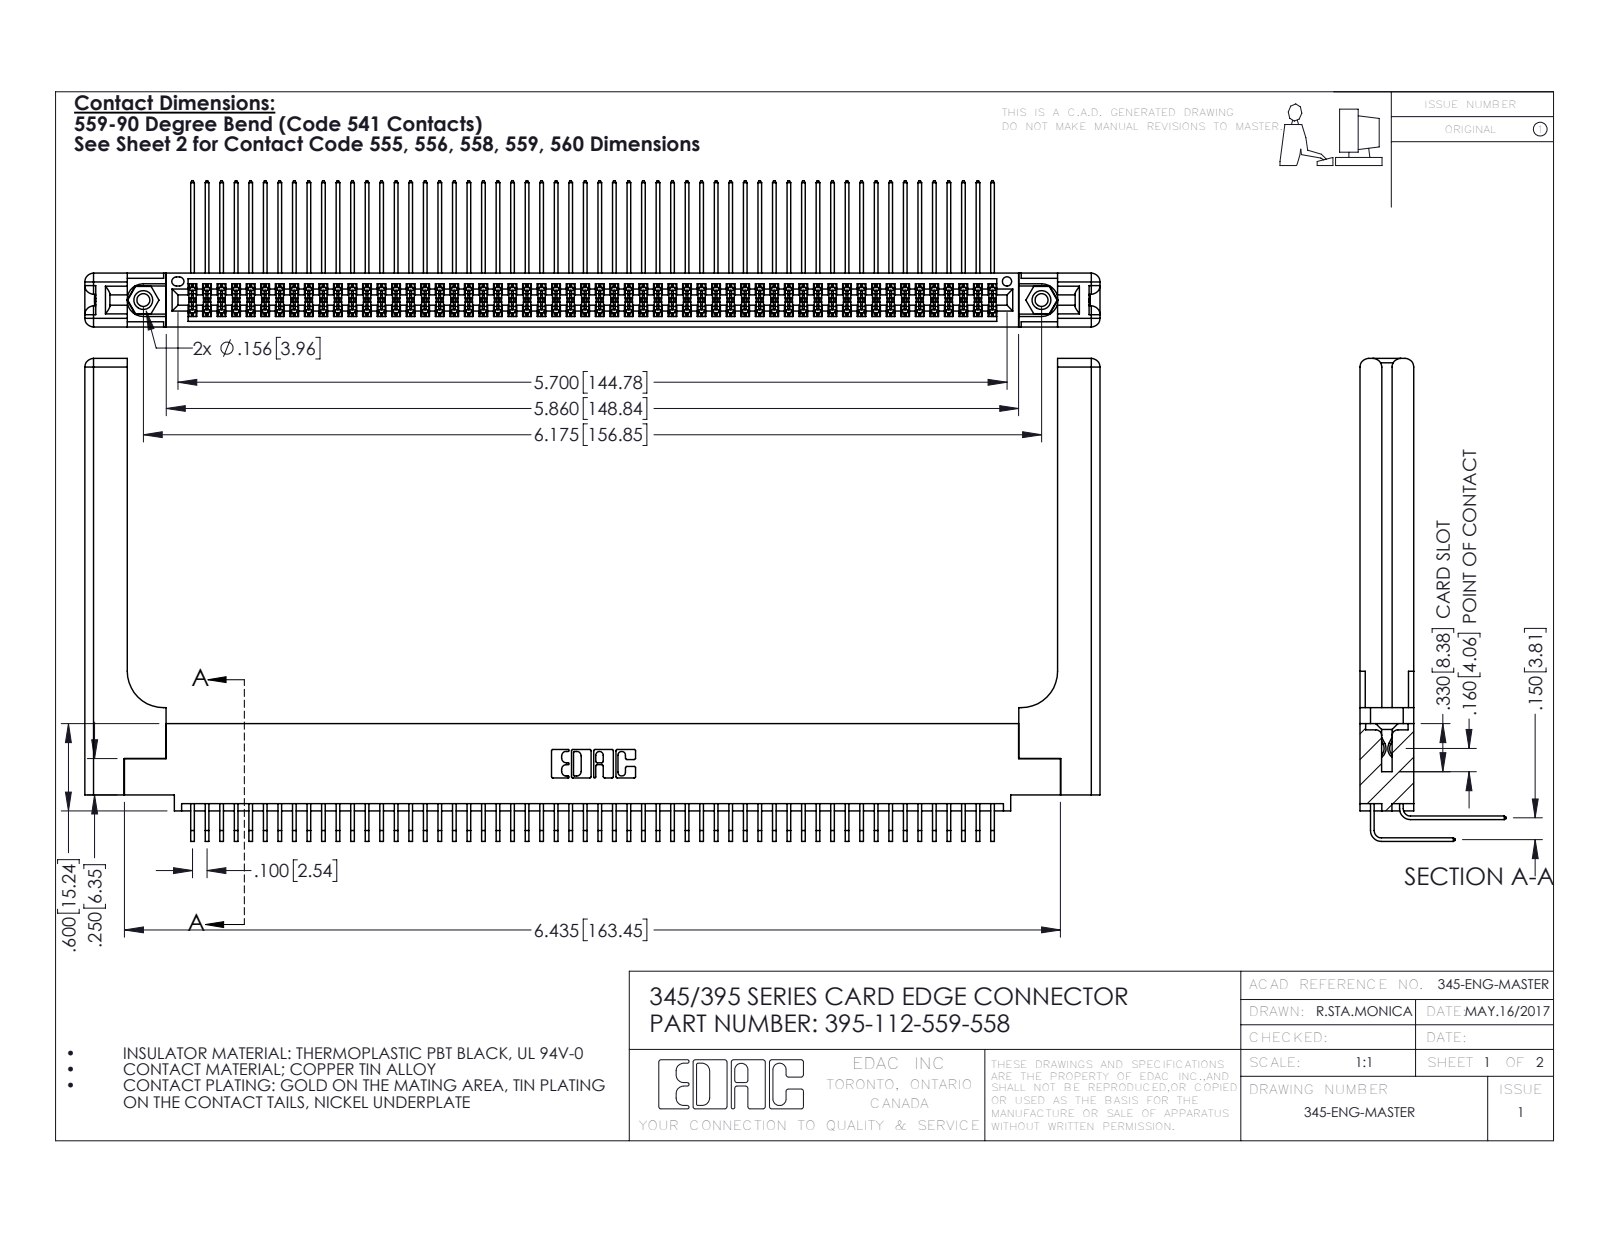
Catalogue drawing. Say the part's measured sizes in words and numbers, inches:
The part is named "395-112-559-558; 345-292-001_559 Tail - 2; 345-292-001_558 559 Tail - 1; 345-250-001_345-250-001-102 (+2 more)". Its 3-D file was written by "SolidWorks 2016 (CONFIG_CONTROL_DESIGN)". It is 117 solids with 6210 faces: 4152 planar, 1998 cylindrical and 60 other. Overall it measures 6.979 by 3.319 by 1.005 inches. Its volume is 1.611 cubic inches and its surface area 54.18 square inches. Round holes: 2 of diameter 0.089, 2 of diameter 0.125, 2 of diameter 0.156, 1 of diameter 0.064. Round bosses or shafts: 2 of diameter 0.155. Partial cylindrical surfaces (rounded edges, fillets, slot ends): 168 of radius 0.006, 22 of radius 0.01, 16 of radius 0.06, 6 of radius 0.007, 6 of radius 0.031, 3 of radius 0.026, 2 of radius 0.014, 2 of radius 0.019. The main face-to-face distances are 0.072, 0.298, 0.37, 0.098, 0.272, 0.025, 0.2, 0.225, 0.175, 0.15. The hole center spacings are 0.27, 5.939, 6.175.
